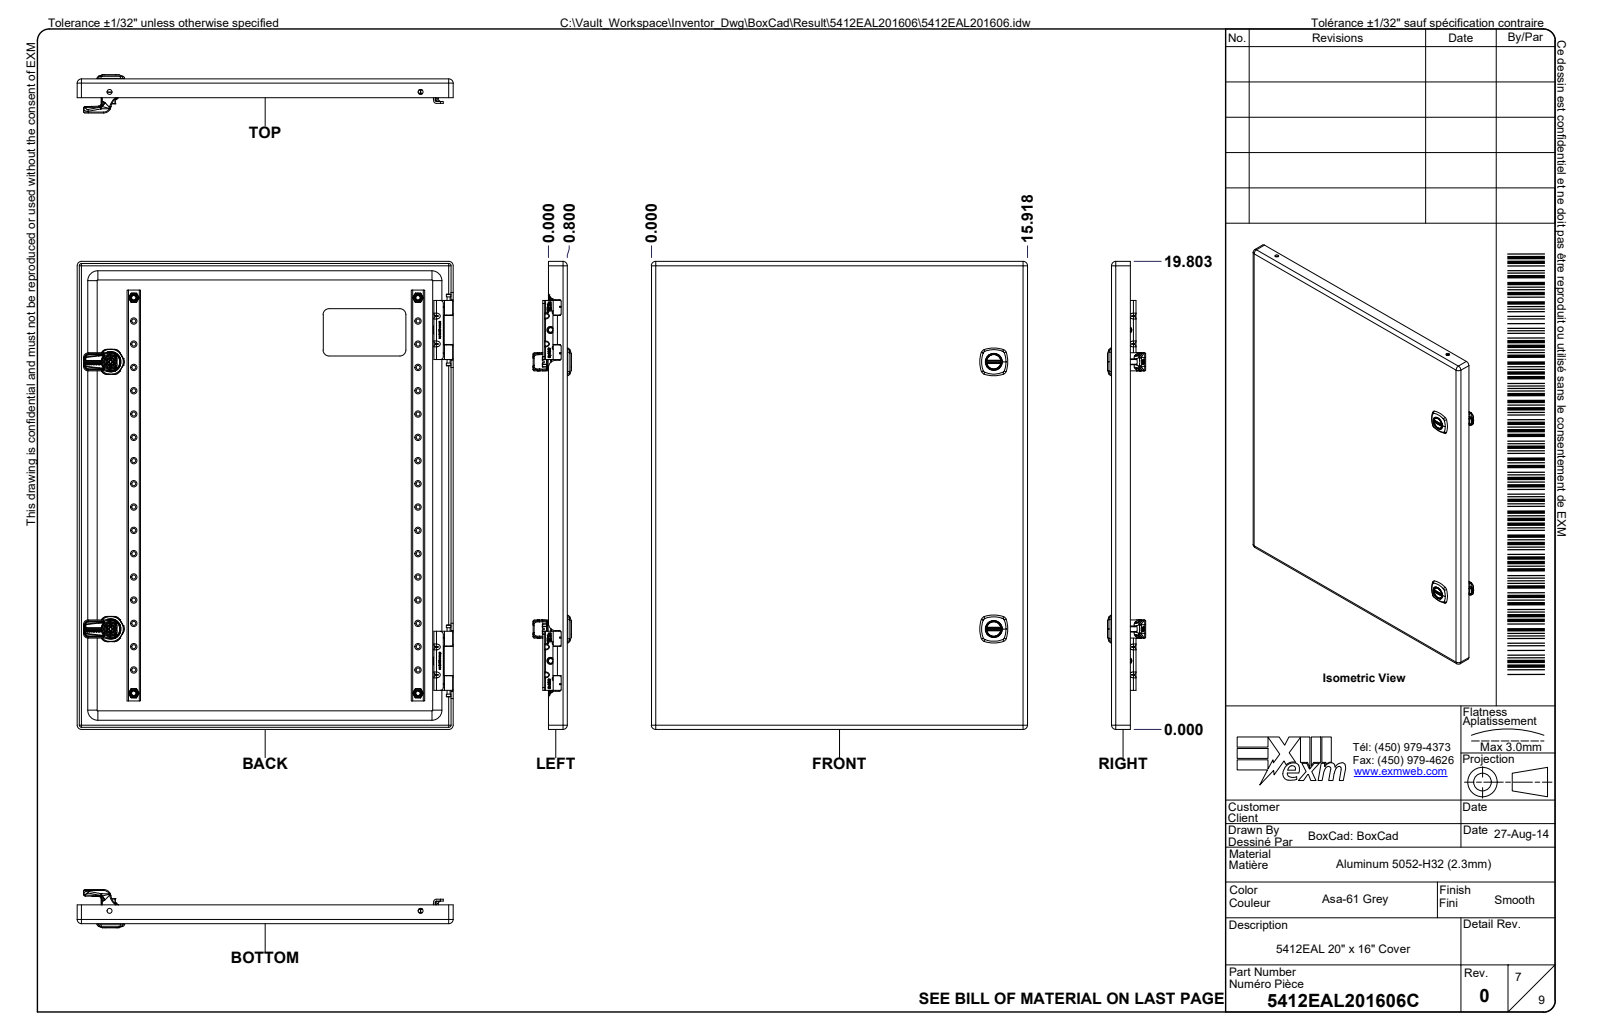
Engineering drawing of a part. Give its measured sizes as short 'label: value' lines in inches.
name: 5412EAL201606; 5412EAL201606B; 5412EAL201606B-P; STK-Q-16010 (+8 more)
written by: Autodesk Inventor 2024 (AUTOMOTIVE_DESIGN)
unit: in
bodies: 64 solids, 5936 faces (2799 planar, 1189 cylindrical, 1948 other)
size: 20 × 16.042 × 7.239
volume: 146.5 in³; area: 3 260 in²
holes: 32× ⌀0.165, 9× ⌀0.03, 8× ⌀0.201, 6× ⌀0.29, 6× ⌀0.311, 6× ⌀0.315, 4× ⌀0.044, 4× ⌀0.197, 4× ⌀0.268, 4× ⌀0.27, 4× ⌀0.39, 4× ⌀0.5
bosses: 32× ⌀0.237, 9× ⌀0.232, 9× ⌀0.03, 8× ⌀0.039, 4× ⌀0.374, 4× ⌀0.311, 2× ⌀0.776, 2× ⌀0.768
rounds: 106× R0.02, 68× R0.008, 64× R0.039, 50× R0.012, 30× R0.031, 28× R0.01, 24× R0.121, 23× R0.125
face distances: 0.09, 6.978, 6.888, 7.068, 0.964, 0.874, 6.014, 6.104, 0.105, 1.069
hole spacings: 0.984, 1.969, 2.953, 3.937, 4.921, 5.906, 6.89, 7.874
